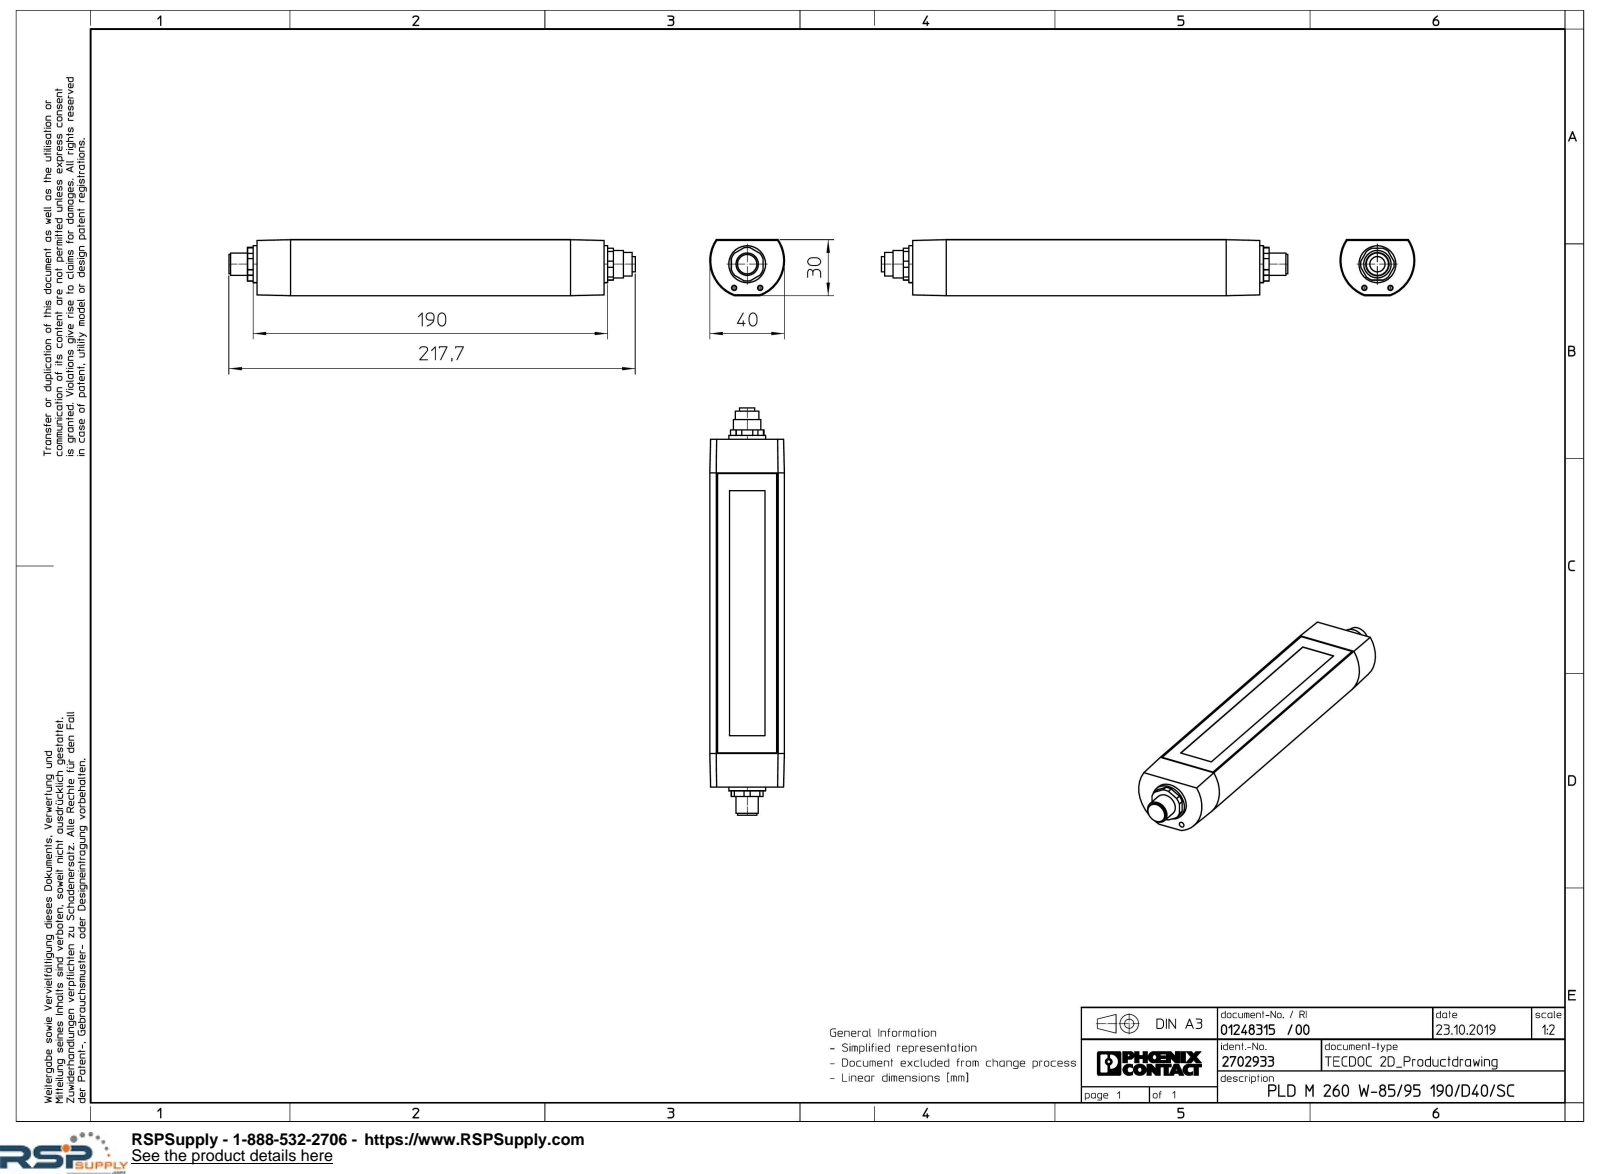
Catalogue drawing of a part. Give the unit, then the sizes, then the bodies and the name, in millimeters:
Units: millimetres
Overall size (bounding box): 217.7 × 40 × 29.95
Round holes (diameter × count): ⌀12 ×1
Round bosses / shafts (diameter × count): ⌀19.75 ×1, ⌀14.7 ×1, ⌀12.5 ×1, ⌀10.4 ×1, ⌀8.2 ×1
Partial cylindrical surfaces — rounded edges, fillets, slot ends (radius × count): R9 ×1, R20 ×1
Main face-to-face distances: 29.75, 29.85, 186, 29.95, 33.55, 33.53, 5, 191, 3, 193
Volume: 196 259 mm³ · Surface area: 26 675 mm²
Bodies: 1 solid, 86 faces (44 planar, 30 cylindrical, 12 other)
Part name (STEP PRODUCT): PLD_M_260_W_85_95_190_D40_SC-select
STEP written by: Creo Elements/Direct Modeling 20.1A 29-Sep-2018 (C) Parametric Technology GmbH (AUTOMOTIVE_DESIGN)
